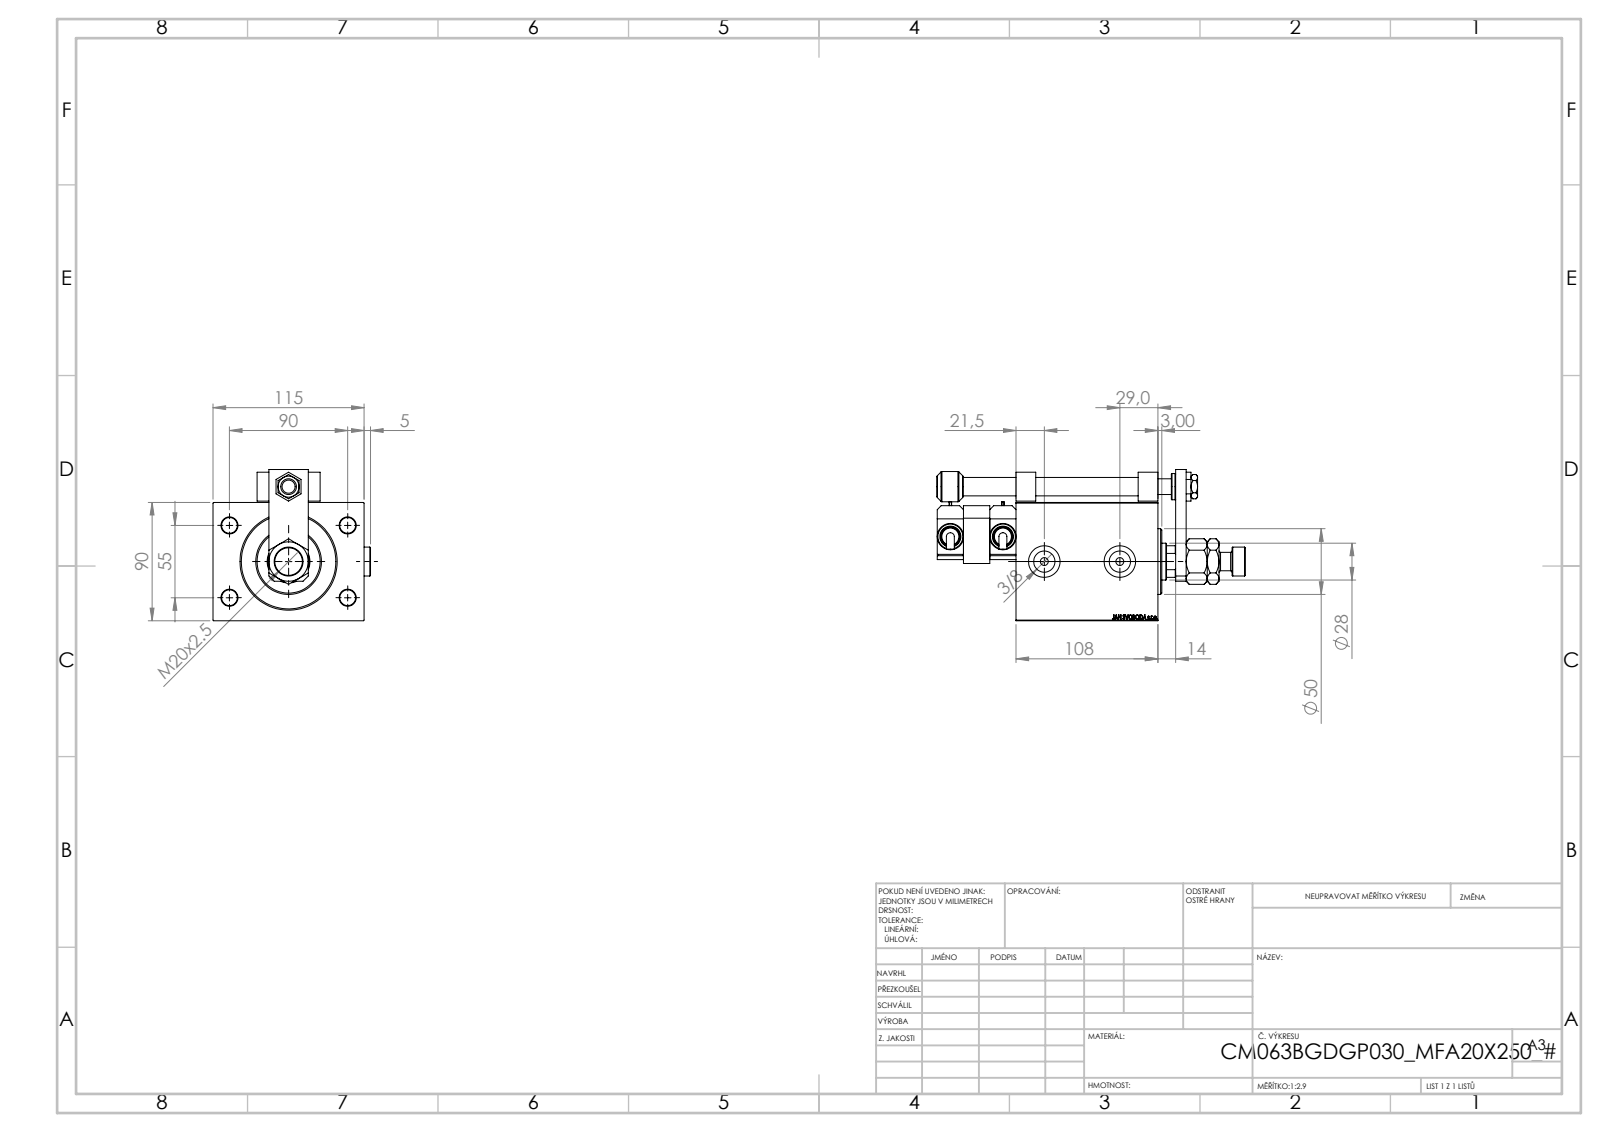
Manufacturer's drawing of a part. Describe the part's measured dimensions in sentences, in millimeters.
The part is named "TYC_P; SWITCH P; KROUZEK_PRO_TYC; V450CM_B_Body (+7 more)". Its 3-D file was written by "SolidWorks 2019 (CONFIG_CONTROL_DESIGN)". It is 17 solids with 1215 faces: 564 planar, 134 cylindrical and 517 other. Overall it measures 234.8 by 119.9 by 115 millimeters. Its volume is 1 219 000 cubic millimeters and its surface area 184 596 square millimeters. Round holes: 5 of diameter 12, 4 of diameter 4, 4 of diameter 8, 2 of diameter 6, 2 of diameter 16.17, 2 of diameter 24, 1 of diameter 13, 1 of diameter 14, 1 of diameter 18.5, 1 of diameter 20, 1 of diameter 28, 1 of diameter 31.5. Round bosses or shafts: 3 of diameter 22, 3 of diameter 20, 3 of diameter 14, 2 of diameter 16, 2 of diameter 6, 1 of diameter 50, 1 of diameter 23. Partial cylindrical surfaces (rounded edges, fillets, slot ends): 1 of radius 3, 1 of radius 13.5. The main face-to-face distances are 90, 115, 108, 20, 17.5, 37.5, 90.5, 35, 40, 13.5. The hole center spacings are 52.74, 20, 53.81, 55, 90, 93, 95.13, 95.74.
